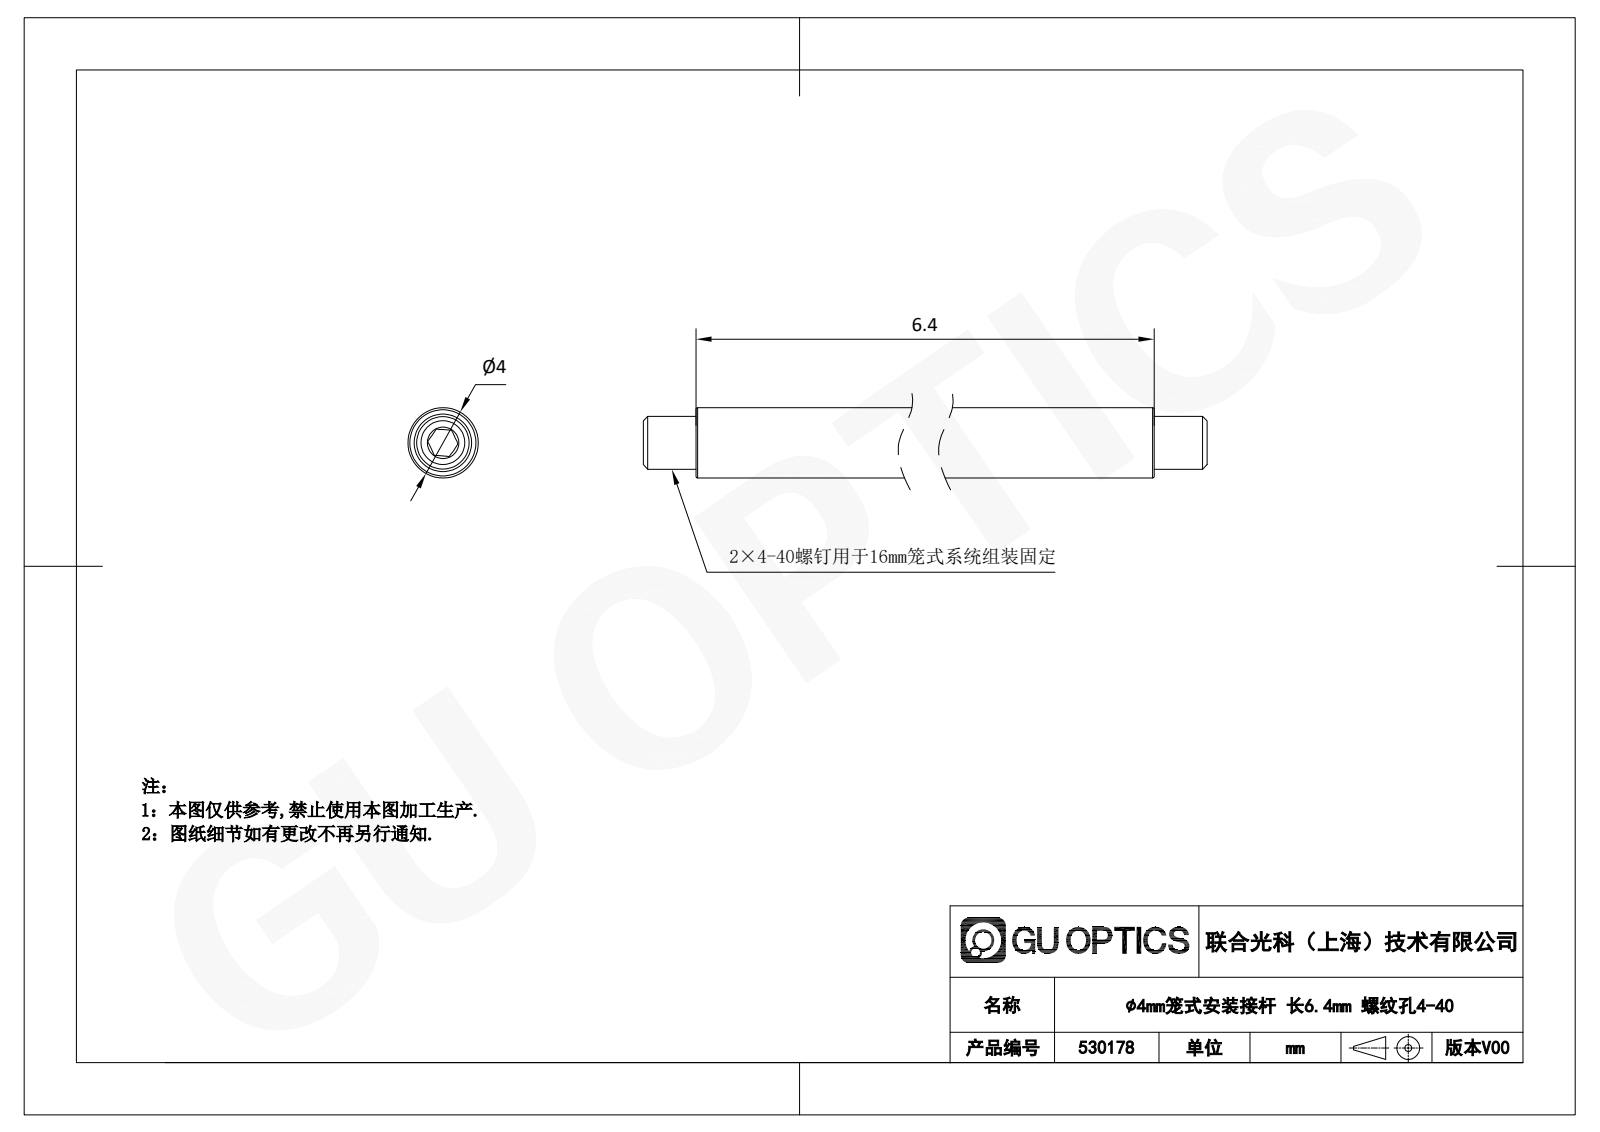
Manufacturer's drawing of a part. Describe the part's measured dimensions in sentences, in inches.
The part is named "530178". Its 3-D file was written by "SolidWorks 2020 (CONFIG_CONTROL_DESIGN)". It is 3 solids with 34 faces: 20 planar, 4 cylindrical and 10 other. Overall it measures 0.644 by 0.157 by 0.157 inches. Its volume is 0.009 cubic inches and its surface area 0.498 square inches. Round holes: 1 of diameter 0.098. Round bosses or shafts: 1 of diameter 0.157, 1 of diameter 0.118. The main face-to-face distances are 0.118, 0.132, 0.197, 0.315, 0.329, 0.447, 0.059, 0.25, 0.039, 0.604.
